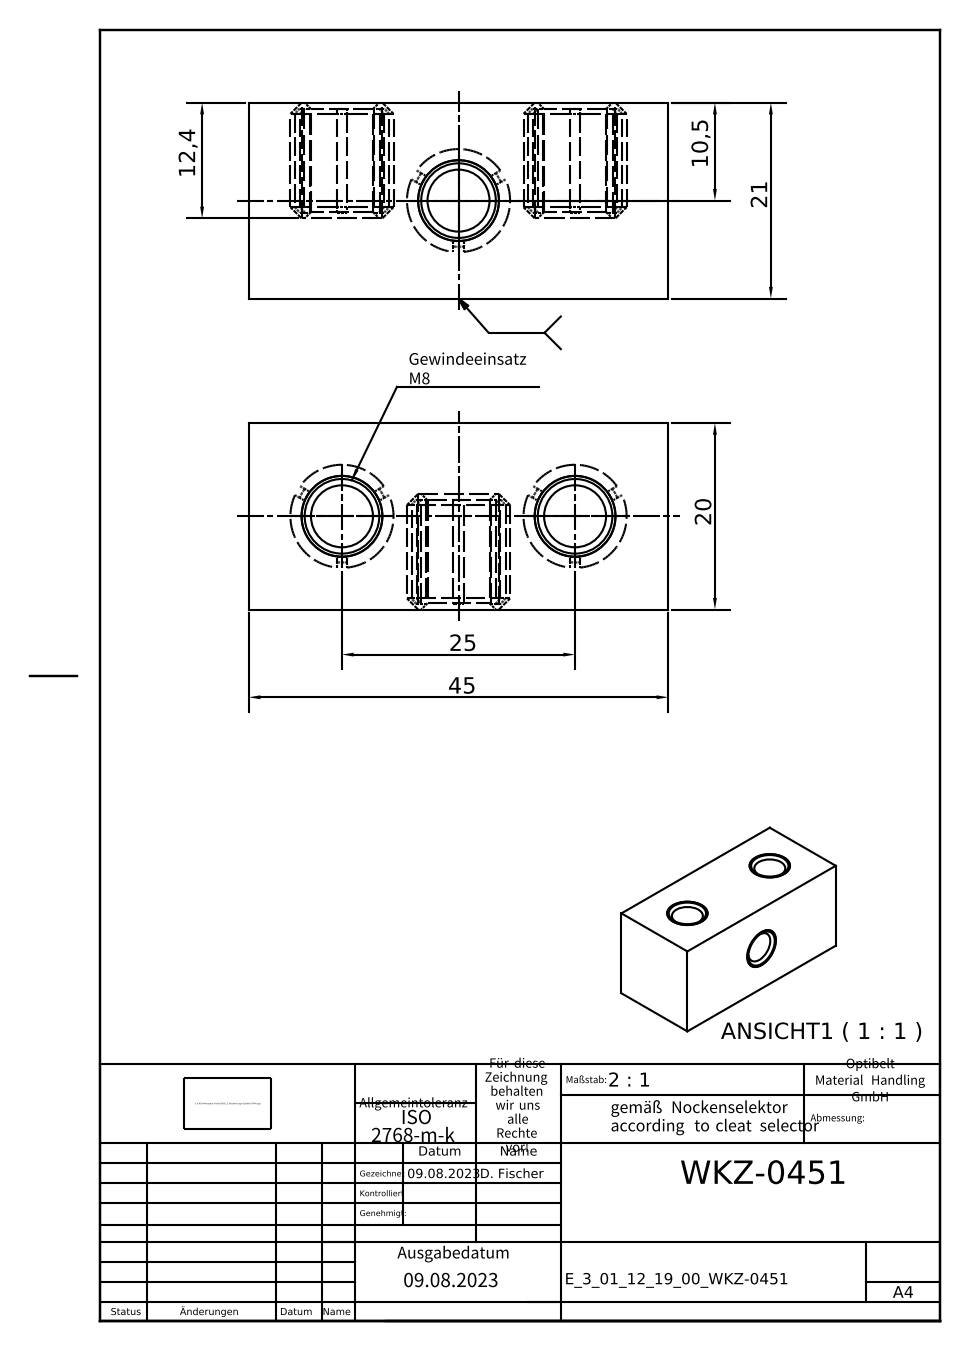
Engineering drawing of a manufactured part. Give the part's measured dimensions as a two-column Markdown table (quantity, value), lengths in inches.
| quantity | value |
| --- | --- |
| part name | E_3_01_12_19_00_WKZ-0451; E_3_01_12_19_00_WKZ-0451_KVT 136M8 |
| STEP written by | Autodesk Inventor 2021 (AUTOMOTIVE_DESIGN) |
| units | inches |
| bodies | 4 solids, 87 faces (60 planar, 15 cylindrical, 12 other) |
| overall size | 1.772 × 0.827 × 0.787 |
| volume | 1.141 in³ |
| surface area | 12.42 in² |
| round holes (diameter × count) | 0.262 × 3, 0.341 × 3 |
| round bosses / shafts (diameter × count) | 0.435 × 3 |
| main face-to-face distances | 0.787, 0.827, 1.772, 0.488, 0.339, 0.492, 0.043, 0.299, 0.535, 0.449 |
| hole center spacings | 0.984 |
